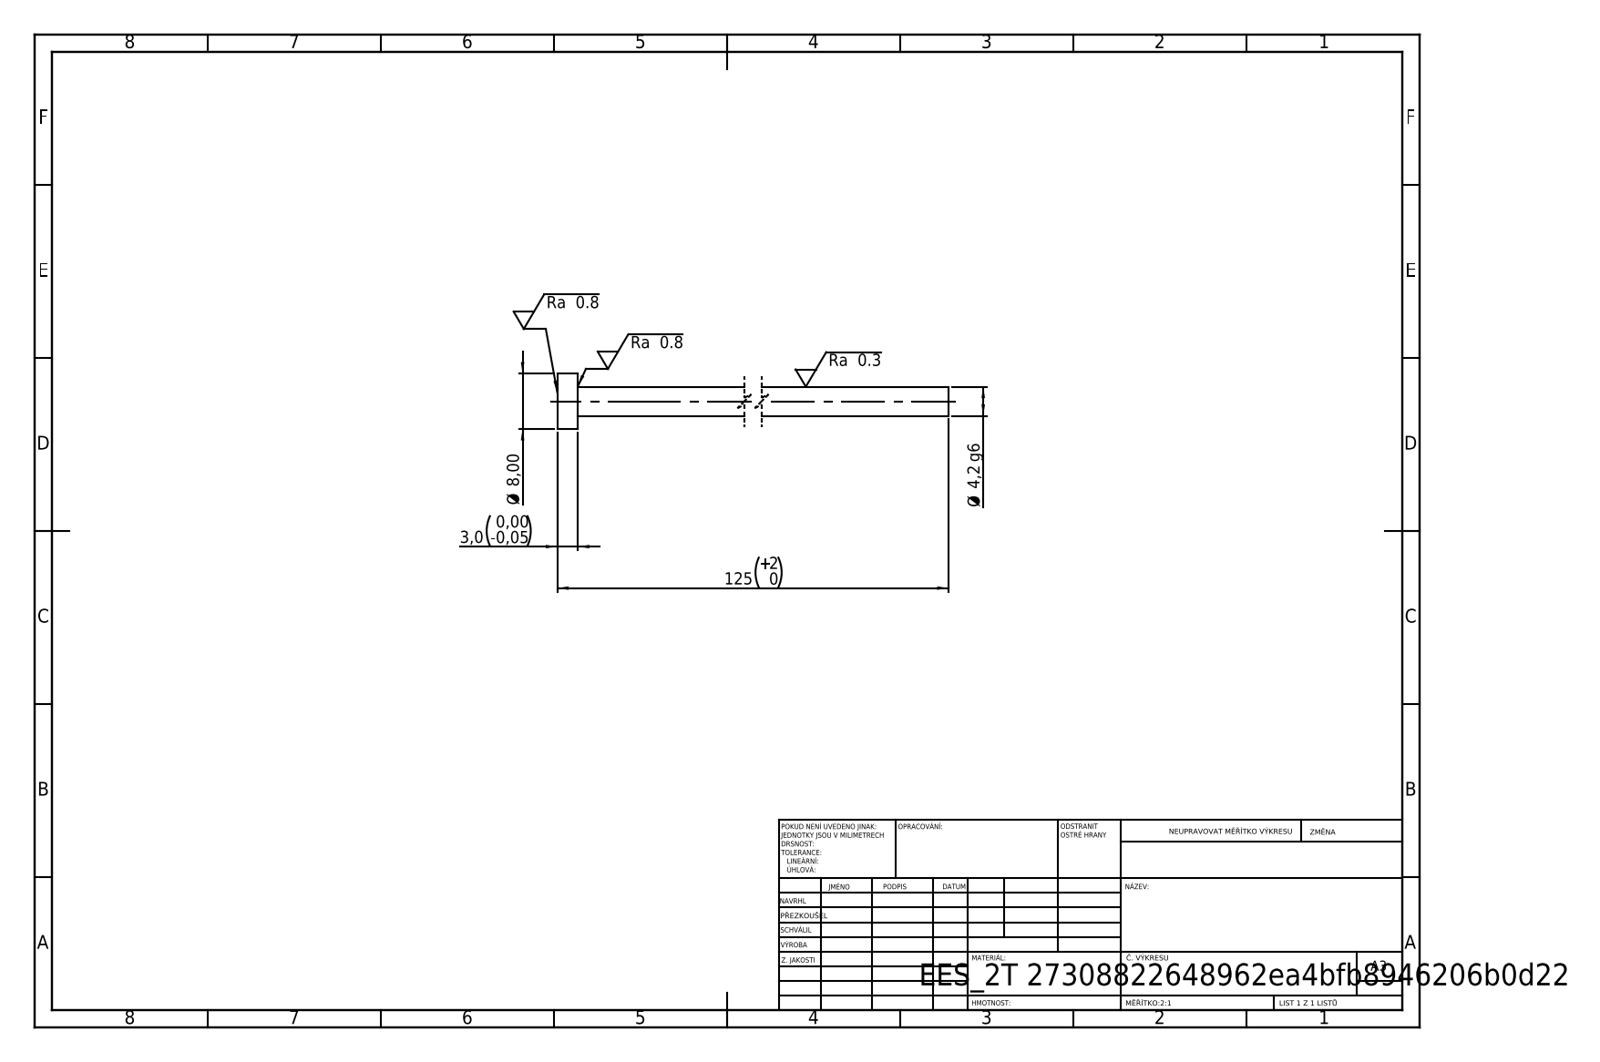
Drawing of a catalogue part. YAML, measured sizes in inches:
step_written_by: "SolidWorks 2019 (CONFIG_CONTROL_DESIGN)"
units: inches
bodies: {solids: 1, faces: 7, planar: 3, cylindrical: 4, other: 0}
overall_size: [4.921, 0.315, 0.315]
volume: 0.112
surface_area: 2.768
round_bosses_or_shafts:
  - {diameter: 0.315, count: 1}
  - {diameter: 0.165, count: 1}
face_to_face_distances: [0.118, 4.921, 4.803]
